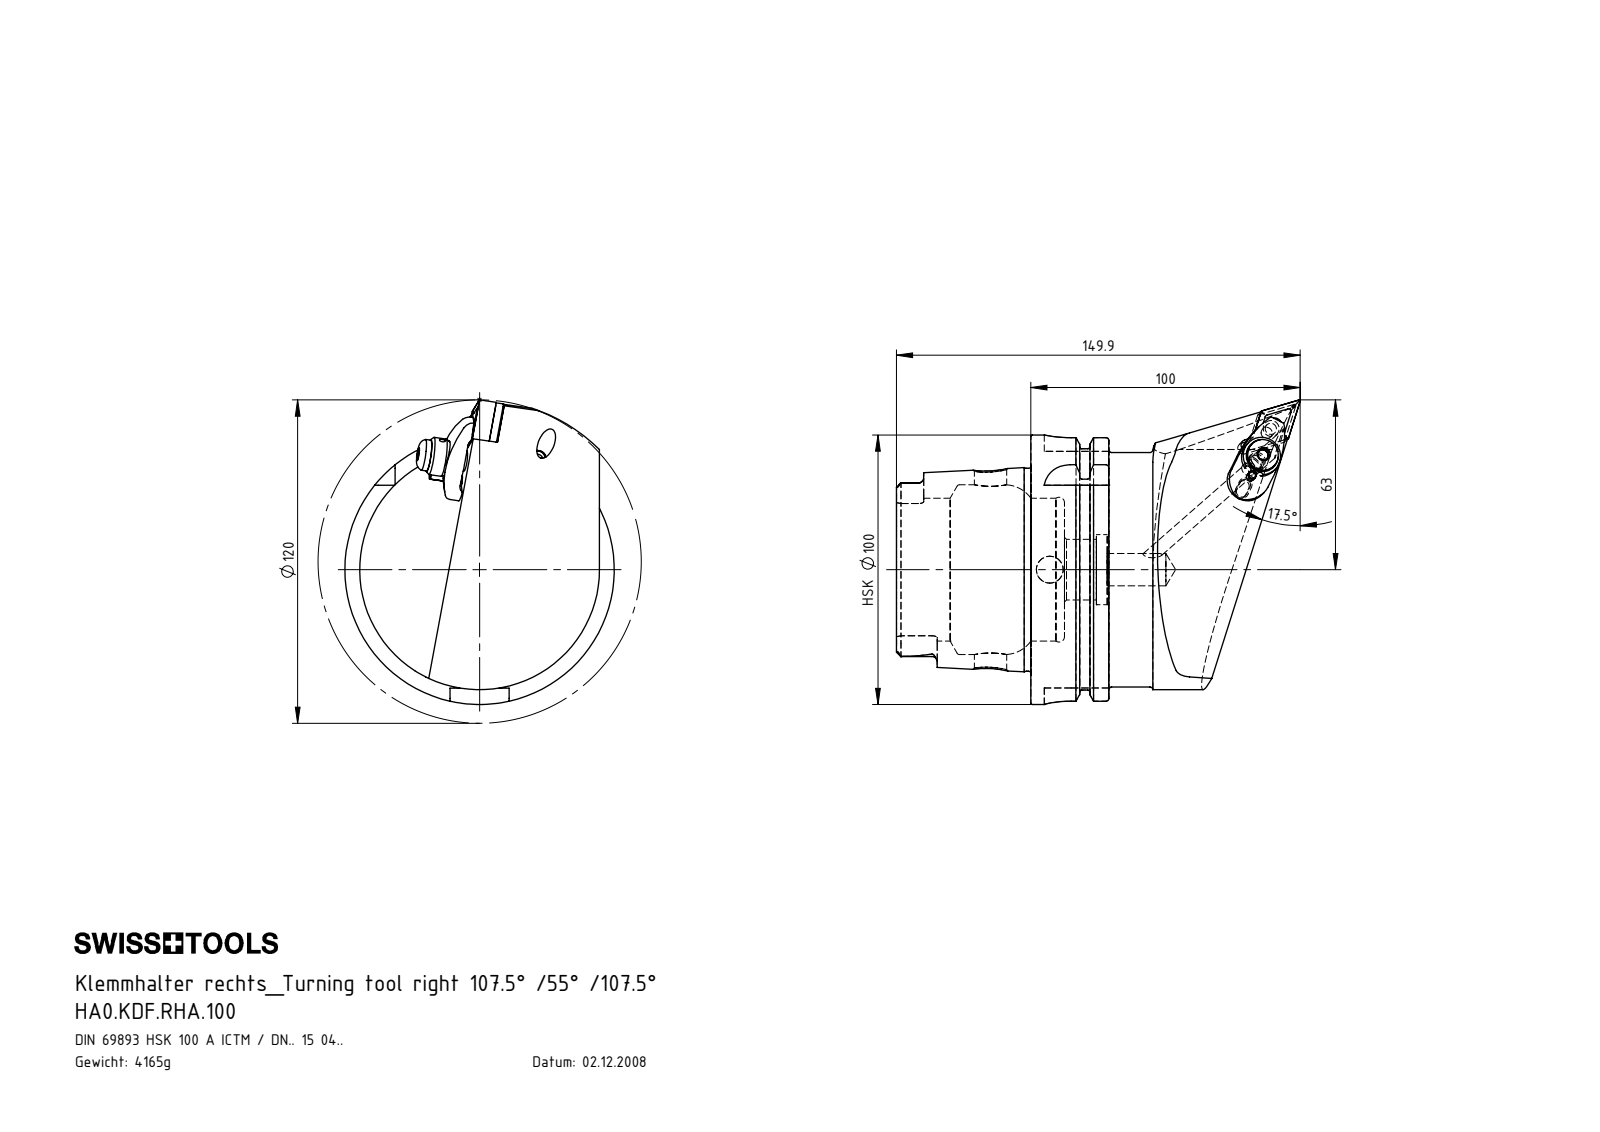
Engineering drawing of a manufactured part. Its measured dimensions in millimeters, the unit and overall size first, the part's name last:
Units: millimetres
Overall size (bounding box): 149.9 × 113 × 100
Round holes (diameter × count): ⌀2 ×3, ⌀5 ×2, ⌀7 ×2, ⌀12 ×2, ⌀2.4 ×1, ⌀3 ×1, ⌀4 ×1, ⌀4.2 ×1, ⌀5.16 ×1, ⌀6 ×1, ⌀6.2 ×1, ⌀6.5 ×1
Round bosses / shafts (diameter × count): ⌀5 ×2, ⌀3 ×2, ⌀100 ×1, ⌀91.95 ×1, ⌀87 ×1, ⌀75.26 ×1, ⌀14 ×1, ⌀11.5 ×1
Partial cylindrical surfaces — rounded edges, fillets, slot ends (radius × count): R0.39 ×6, R0.69 ×6, R1.9 ×6, R0.4 ×5, R10 ×4, R1.5 ×3, R2 ×2, R3 ×2
Main face-to-face distances: 12.45, 28.95, 16.5, 49.9, 62.35, 78.85, 87.8, 78.2, 28.3, 15.85
Hole centre spacings: 7.9, 8.2, 15, 15.1, 22.9, 23, 0.31, 7.89
Volume: 531 537 mm³ · Surface area: 73 106 mm²
Bodies: 11 solids, 463 faces (120 planar, 153 cylindrical, 190 other)
Part name (STEP PRODUCT): HA0.KDF.RHA.100; WCC-ER3.102.024_C; DNMG150604; WDF-ER2.101.003_A (+7 more)
STEP written by: SolidWorks 2017 (AUTOMOTIVE_DESIGN)
